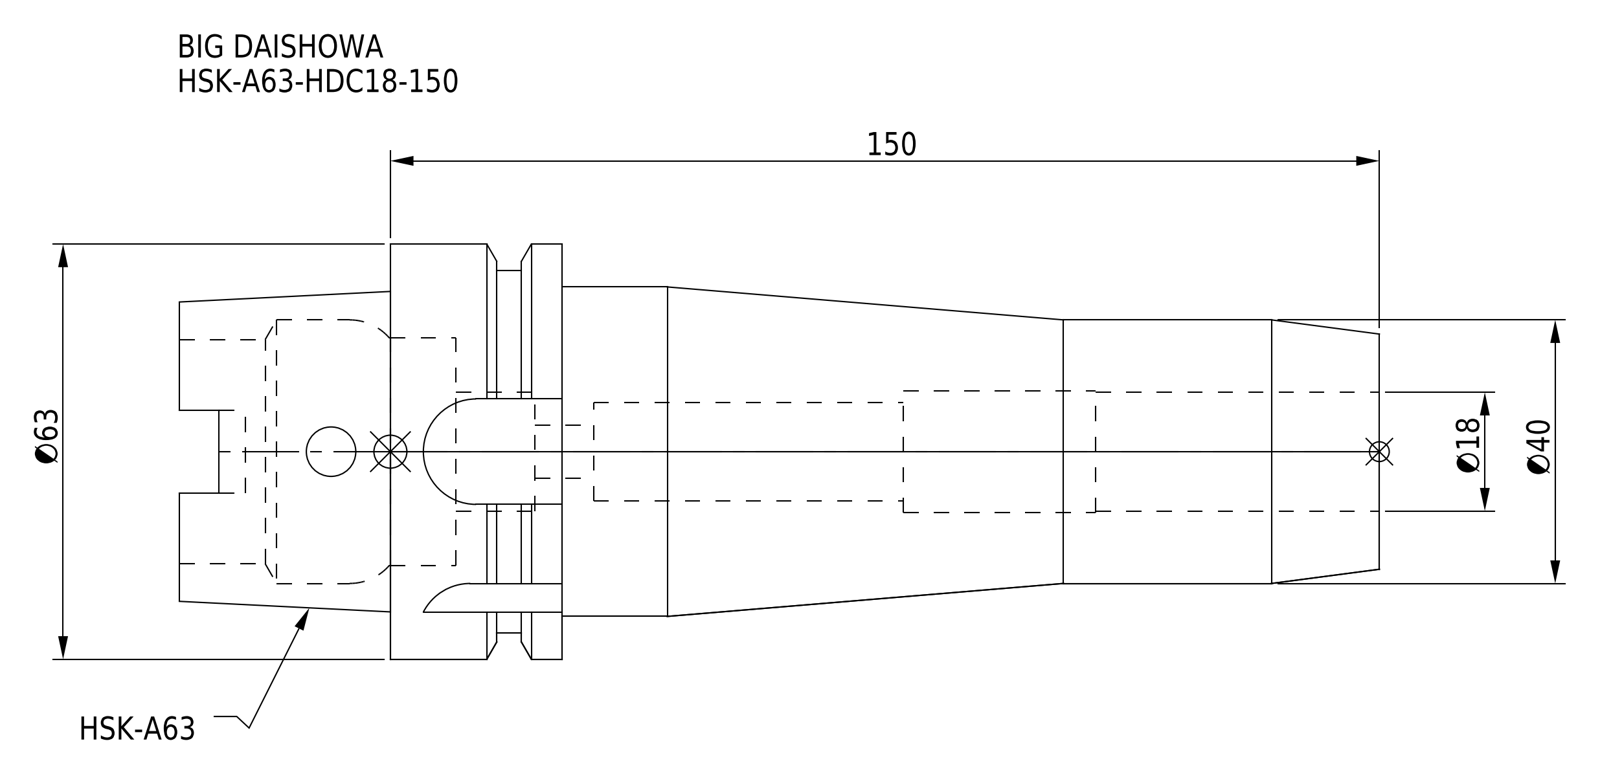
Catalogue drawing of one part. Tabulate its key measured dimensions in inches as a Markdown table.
| quantity | value |
| --- | --- |
| part name | HSK-A63-HDC18-150 |
| STEP written by | CREO PARAMETRIC BY PTC INC, 2016380 (AUTOMOTIVE_DESIGN) |
| units | inches |
| bodies | 1 solid, 98 faces (39 planar, 41 cylindrical, 18 other) |
| overall size | 7.165 × 2.48 × 2.48 |
| volume | 14.63 in³ |
| surface area | 69.46 in² |
| round holes (diameter × count) | 0.295 × 1, 0.315 × 1, 0.591 × 1, 0.709 × 1, 0.728 × 1, 1.339 × 1, 1.358 × 1, 1.575 × 1 |
| round bosses / shafts (diameter × count) | 2.48 × 1, 2.165 × 1, 1.969 × 1 |
| partial cylindrical surfaces (radius × count) | 0.113 × 4, 0.315 × 4 |
| main face-to-face distances | 1.024, 4.882, 5.906, 5.514, 0.632, 0.392, 7.165, 2.283, 1.652, 1.26 |
